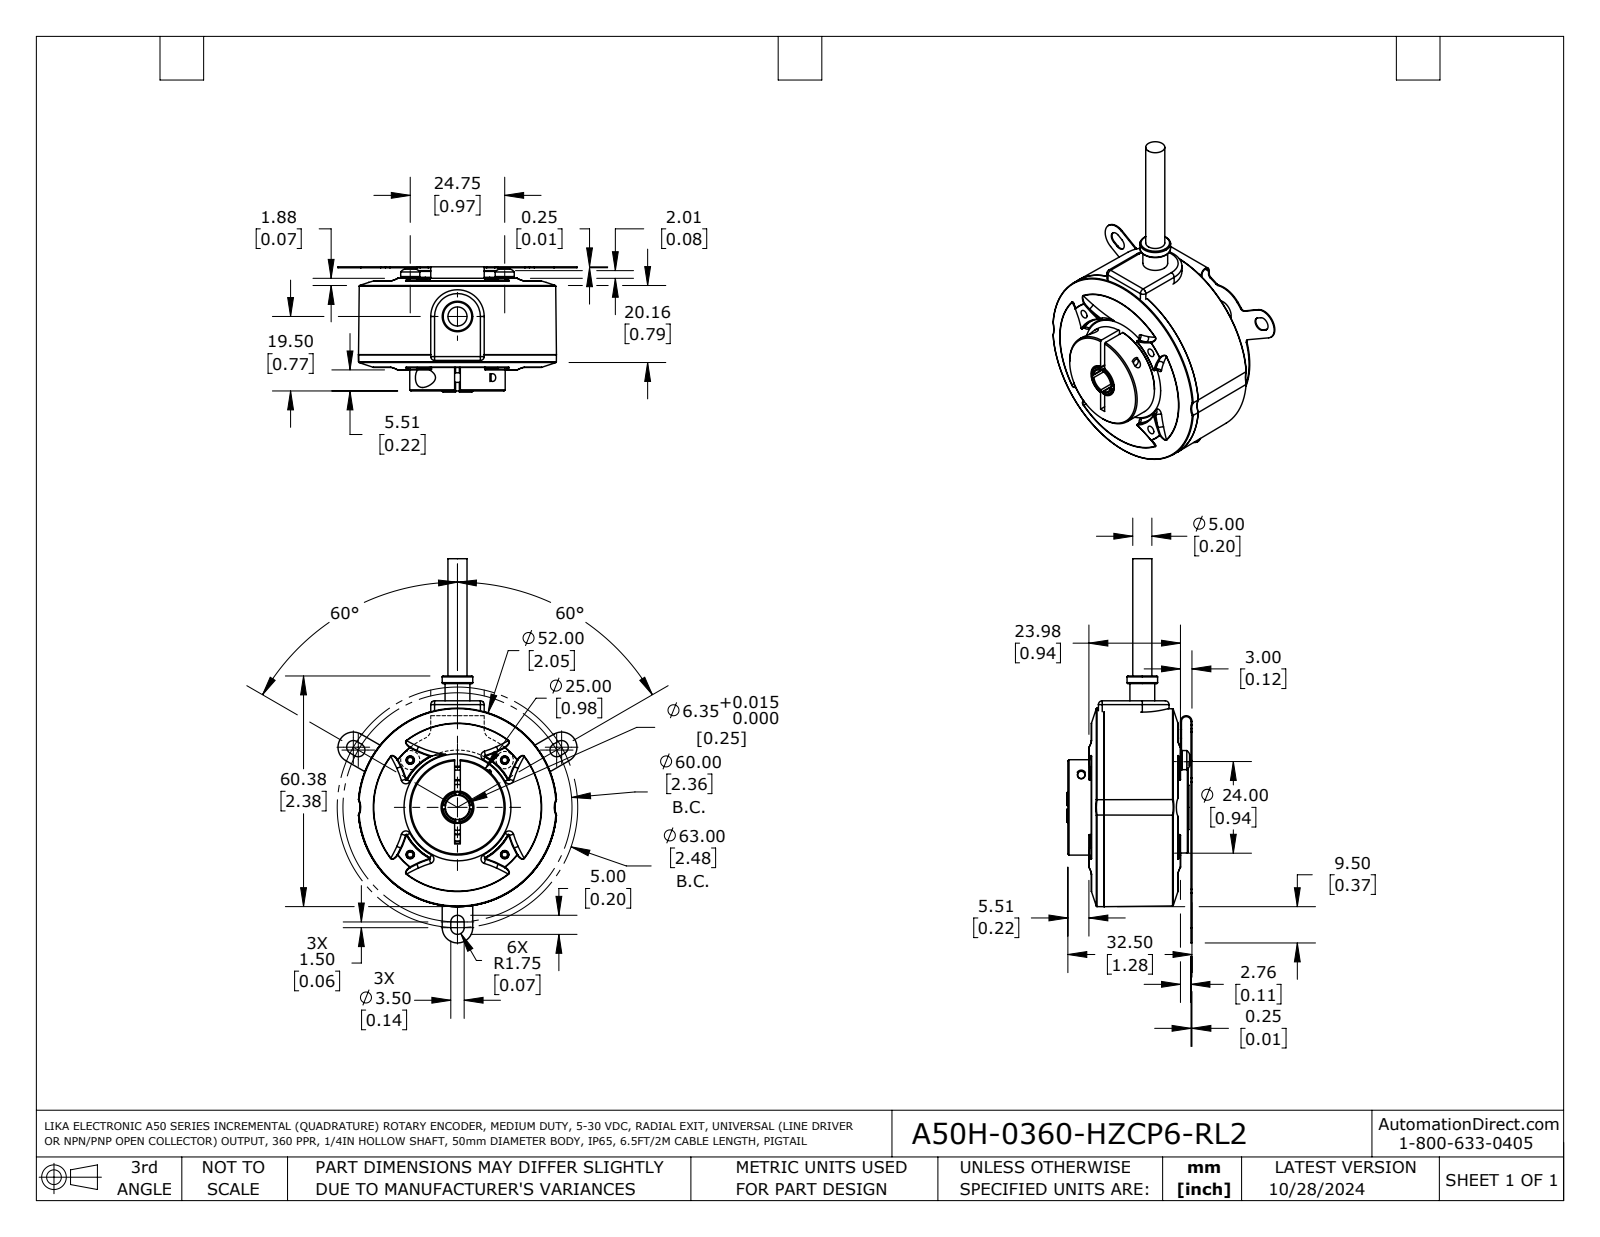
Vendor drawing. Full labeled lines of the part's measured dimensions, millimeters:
Part name (STEP PRODUCT): A50H-0360-HZCP6-RL2
STEP written by: SolidWorks 2021 (AUTOMOTIVE_DESIGN)
Units: millimetres
Bodies: 14 solids, 954 faces (160 planar, 259 cylindrical, 535 other)
Overall size (bounding box): 100.6 × 62.6 × 32.8
Volume: 22 780 mm³ · Surface area: 28 050 mm²
Round holes (diameter × count): ⌀2.8 ×5, ⌀5.5 ×2, ⌀6 ×2, ⌀2.1 ×1, ⌀5.2 ×1, ⌀6.4 ×1, ⌀8 ×1, ⌀14.7 ×1, ⌀18.5 ×1, ⌀26 ×1
Round bosses / shafts (diameter × count): ⌀2.5 ×5, ⌀5 ×4, ⌀25 ×1, ⌀21 ×1, ⌀18 ×1, ⌀14.5 ×1, ⌀12 ×1, ⌀8 ×1
Partial cylindrical surfaces — rounded edges, fillets, slot ends (radius × count): R0.2 ×24, R0.4 ×24, R1 ×18, R0.1 ×6, R1.8 ×6, R25 ×5, R4 ×3, R0.5 ×2
Main face-to-face distances: 3, 2, 20, 5, 17, 22, 22.8, 7, 19, 2.5
Hole centre spacings: 14.8, 17.5, 20.5, 35.1, 24.7, 41
